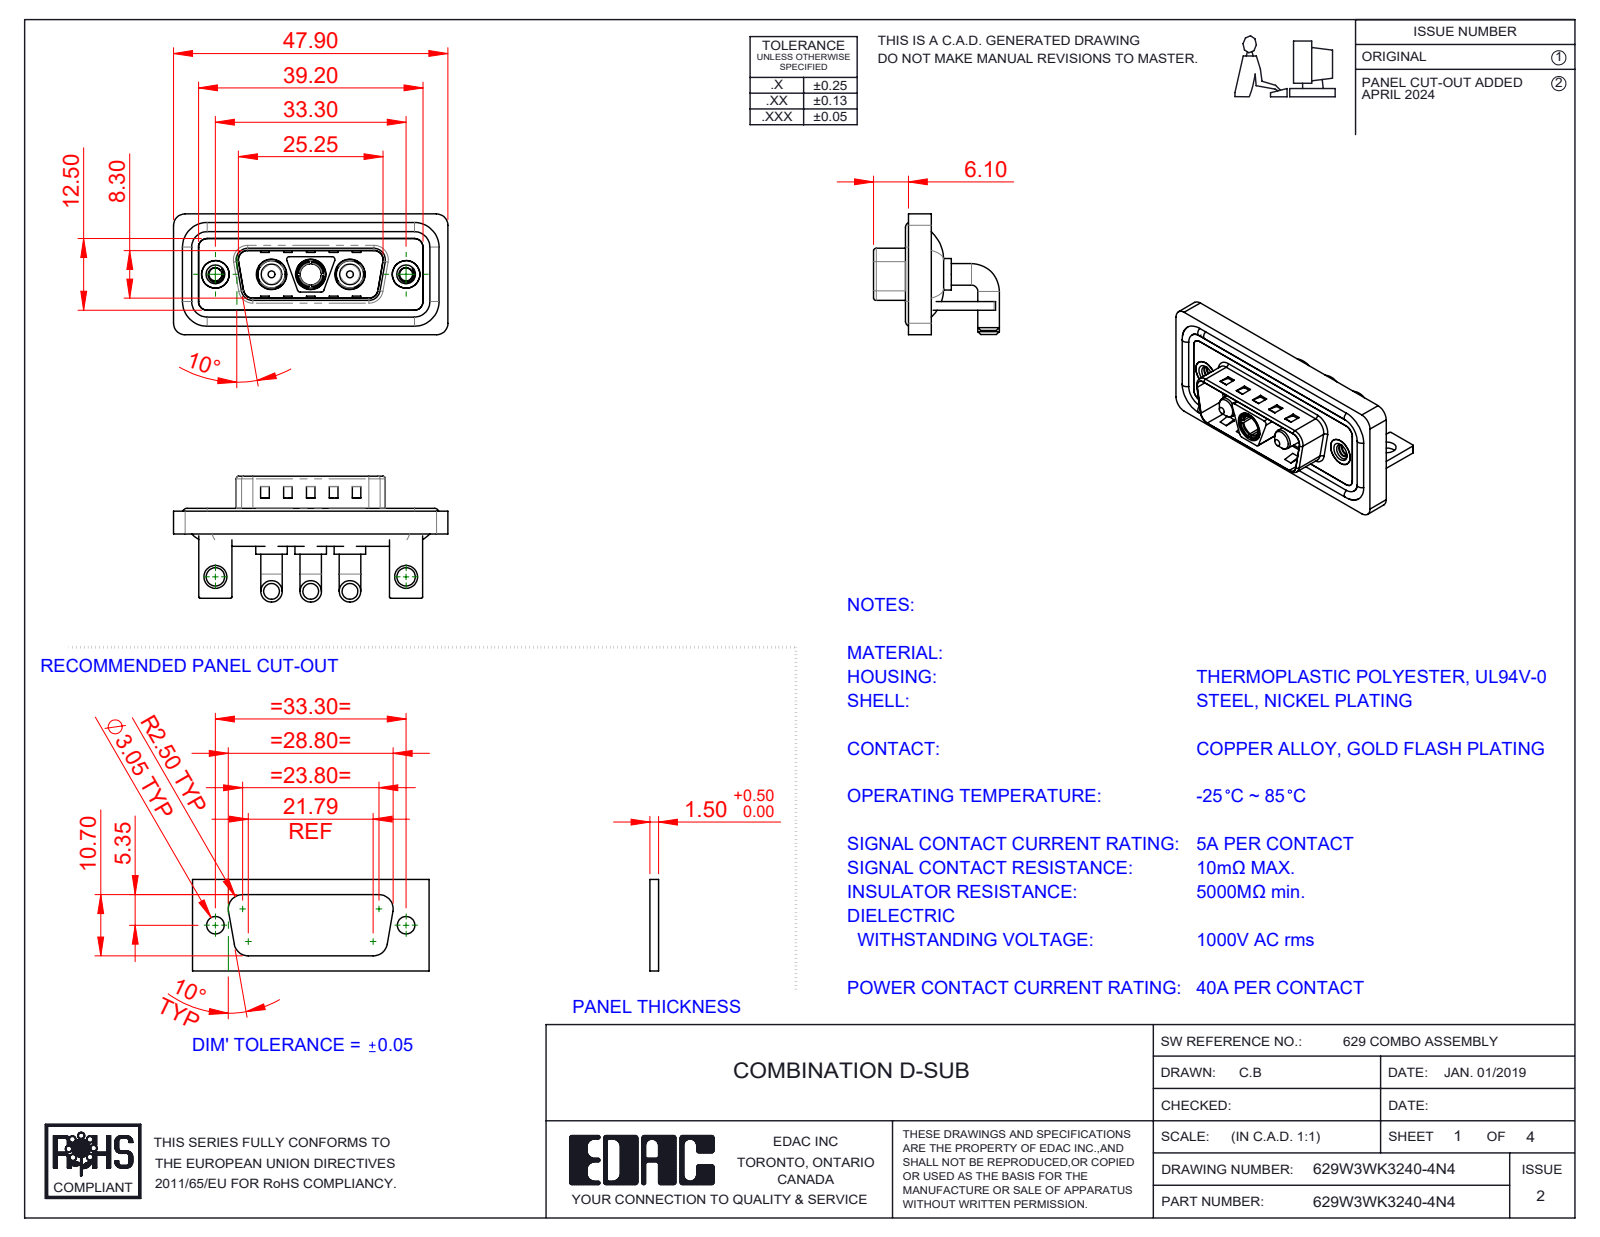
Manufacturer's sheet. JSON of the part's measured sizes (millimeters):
{"part_name": "629Combo Shell Rear_15 Contacts; 629Combo Stabilizer Bracket; 629Combo Shell Front_15 Contacts; 629W3WK3240-4N4 (+5 more)", "step_written_by": "SolidWorks 2023 (CONFIG_CONTROL_DESIGN)", "units": "millimeters", "bodies": {"solids": 15, "faces": 661, "planar": 251, "cylindrical": 274, "other": 136}, "overall_size": [47.9, 21.98, 21.1], "volume_mm3": 6385, "surface_area_mm2": 10136, "round_holes": [[4.85, 3], [5.3, 3], [2.26, 2], [3.2, 2], [4, 2], [4.8, 2], [5, 2], [3.7, 1]], "round_bosses_or_shafts": [[3.75, 6], [1.6, 4], [5.5, 3], [5.2, 3], [4.75, 3], [4.9, 2], [3.6, 2], [4.96, 1]], "partial_cylinders_radius": [[2, 21], [1.5, 18], [0.25, 16], [0.5, 13], [1.6, 8], [0.6, 4], [0.65, 4], [0.9, 4]], "face_to_face_distances": [0.4, 1.5, 0.8, 2.9, 1.1, 2.1, 3.7, 1.6, 1.2, 4.5], "hole_center_spacings": [6.85, 9.8, 16.65, 23.5, 33.3, 13.7]}
